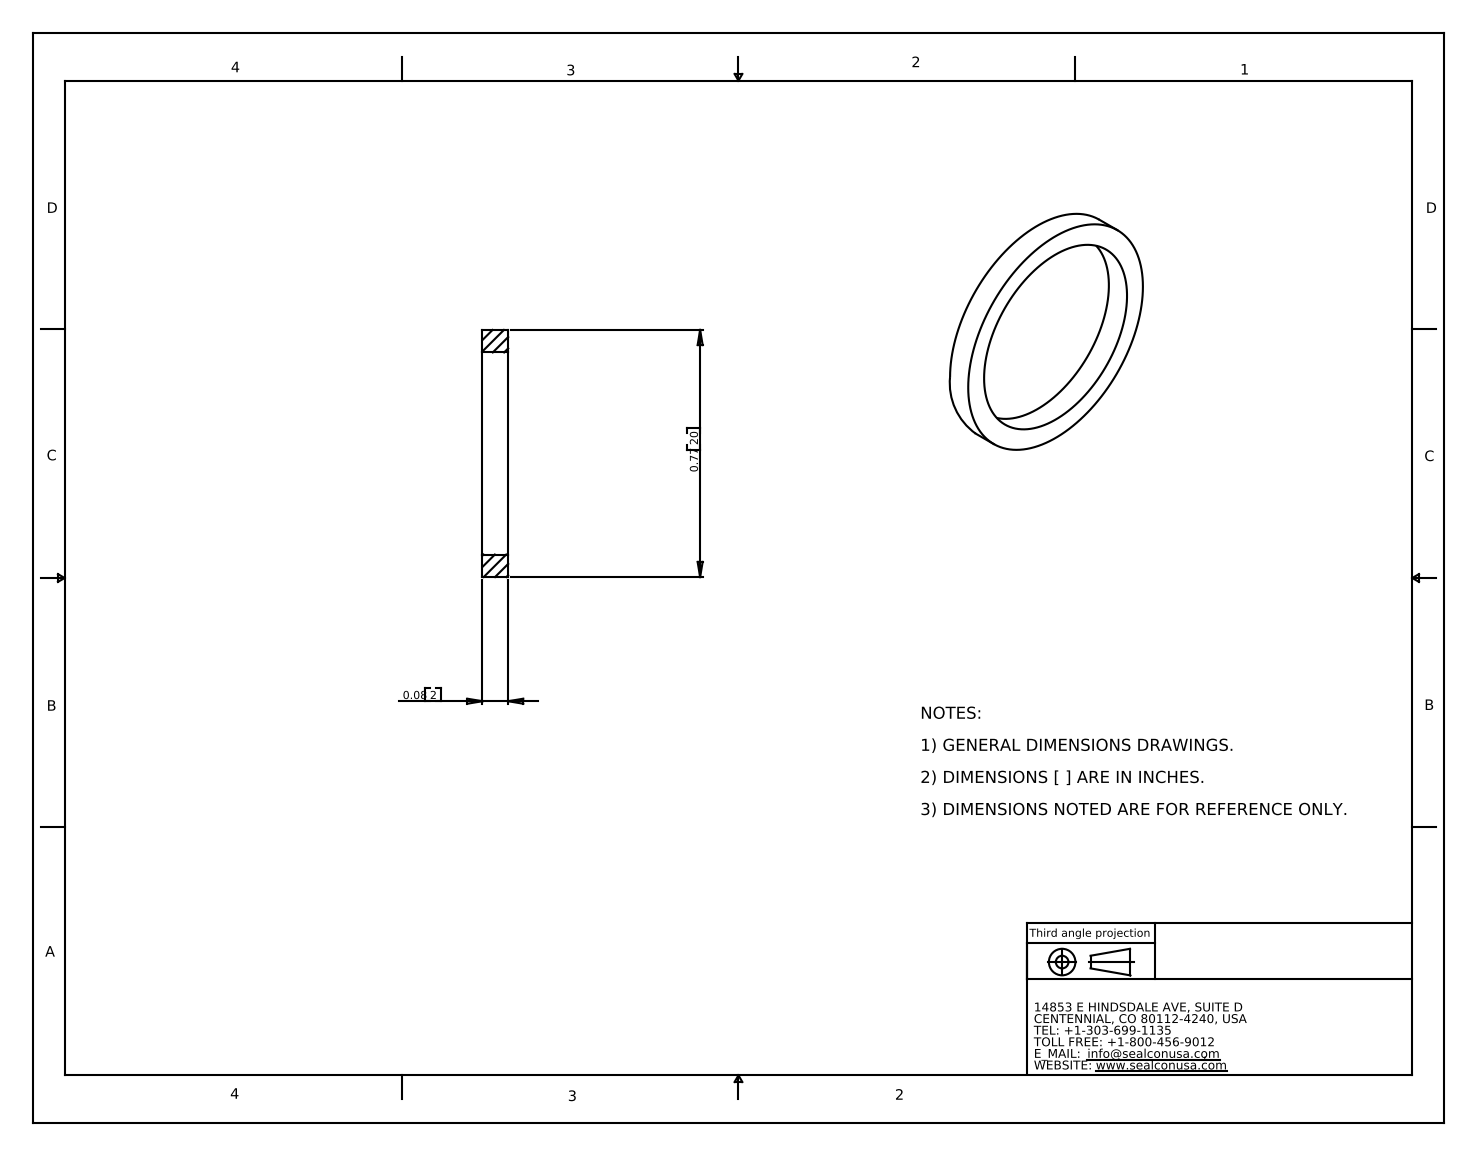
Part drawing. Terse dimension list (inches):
name: SM-16-VT
written by: SolidWorks 2007 (CONFIG_CONTROL_DESIGN)
unit: in
bodies: 1 solid, 6 faces (2 planar, 4 cylindrical, 0 other)
size: 0.77 × 0.77 × 0.08
volume: 0.012 in³; area: 0.66 in²
holes: 1× ⌀0.63
bosses: 1× ⌀0.77
face distances: 0.08
